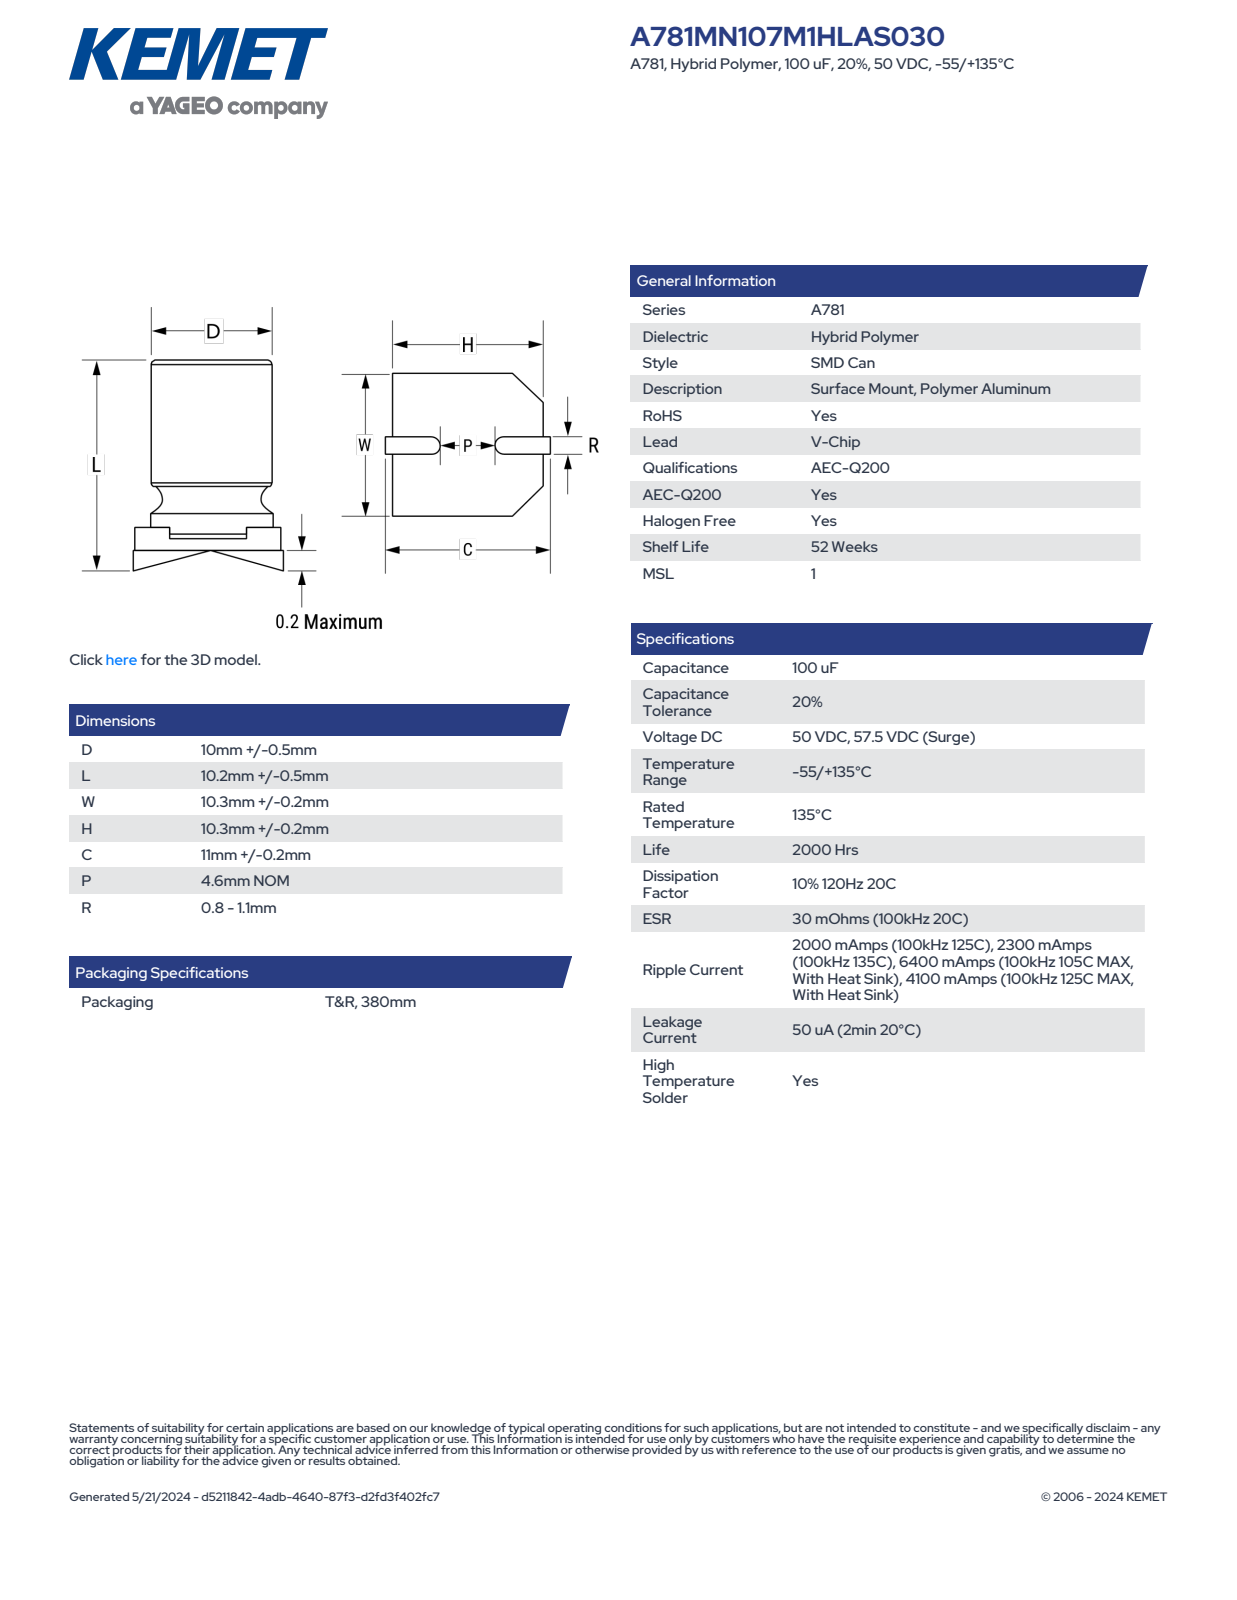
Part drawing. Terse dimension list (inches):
name: CAC_KSA_10X10.2_D10.5L10.7H10.5C11.2P4.6W10.5R1.1
written by: SolidWorks 2021 (AUTOMOTIVE_DESIGN)
unit: in
bodies: 5 solids, 76 faces (59 planar, 11 cylindrical, 6 other)
size: 0.441 × 0.422 × 0.413
volume: 0.053 in³; area: 1.24 in²
bosses: 1× ⌀0.395
rounds: 2× R0.008, 1× R0.164, 1× R0.207
face distances: 0.021, 0.413, 0.393, 0.105, 0.084, 0.308, 0.029, 0.113, 0.421, 0.138
